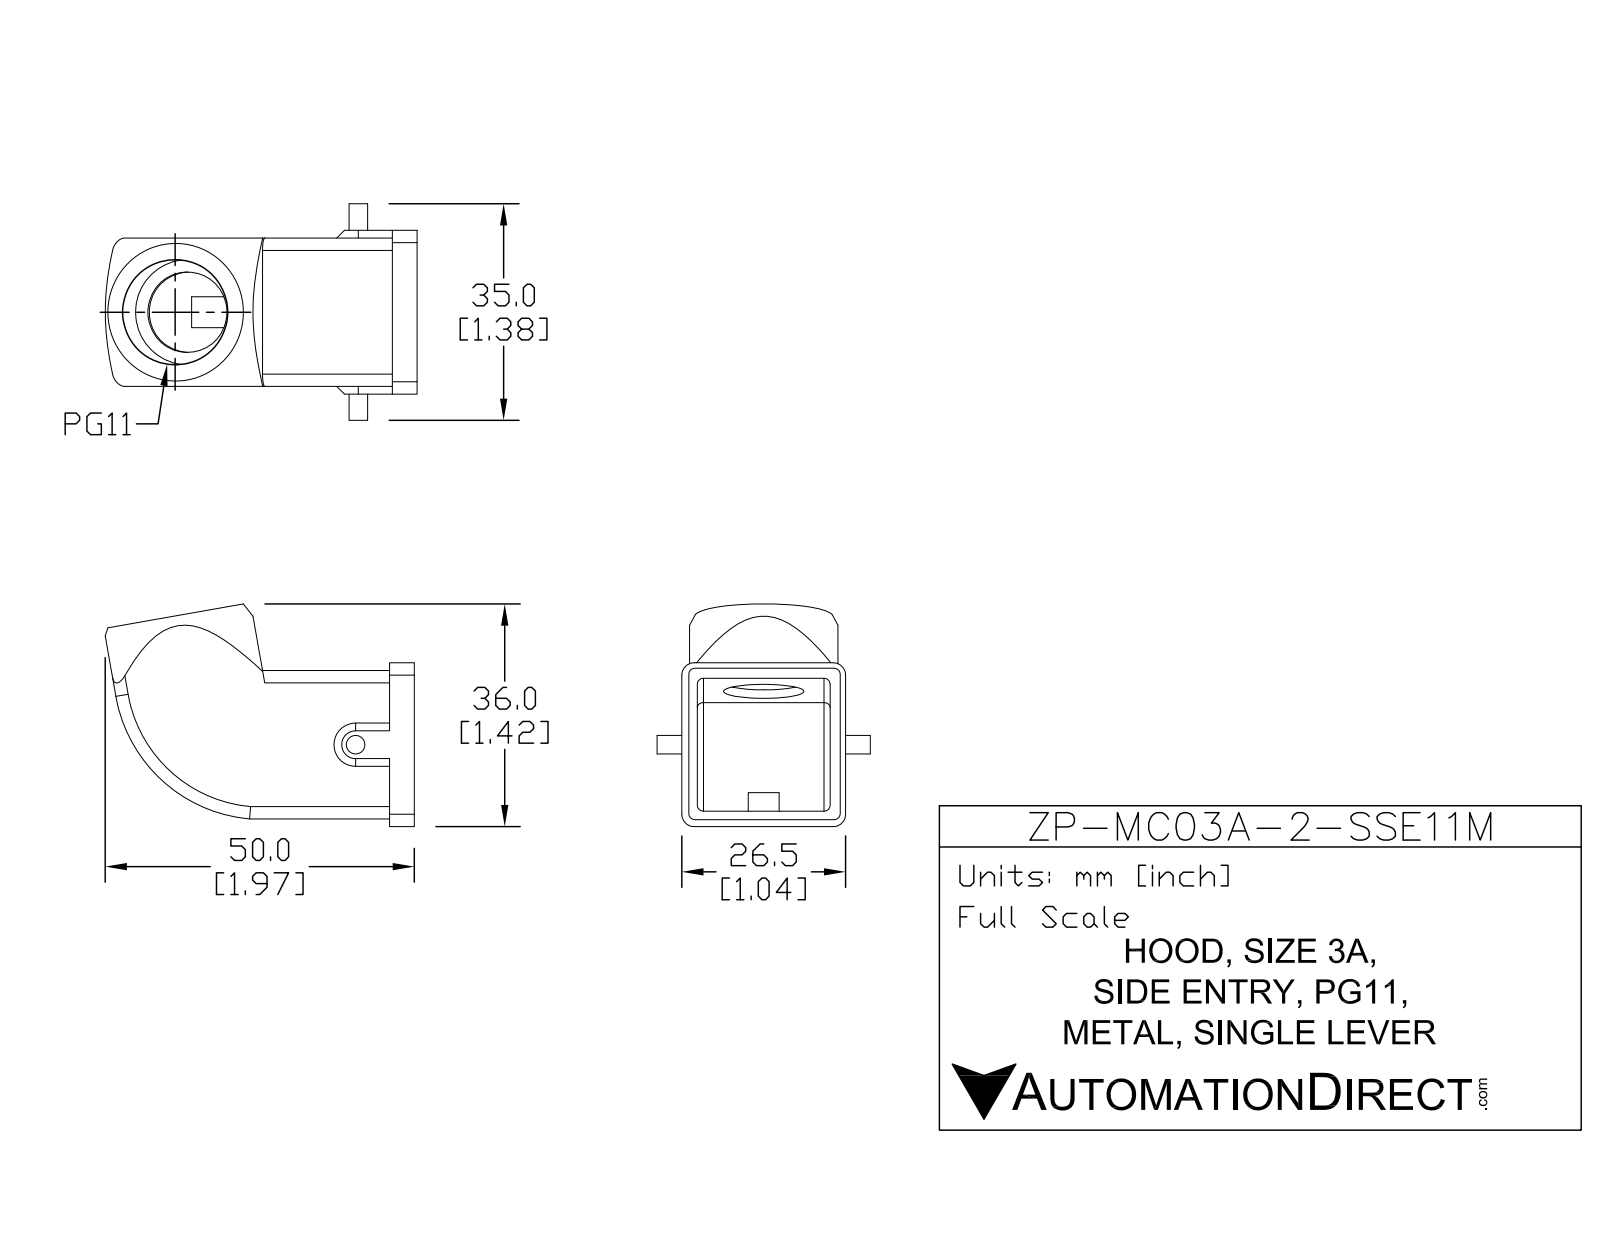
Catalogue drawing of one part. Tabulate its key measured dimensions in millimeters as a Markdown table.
| quantity | value |
| --- | --- |
| part name | ZP-MC03A-2-SSE11M |
| STEP written by | SolidWorks 2011 (AUTOMOTIVE_DESIGN) |
| units | millimeters |
| bodies | 1 solid, 72 faces (37 planar, 27 cylindrical, 8 other) |
| overall size | 47.95 × 36.02 × 34.5 |
| volume | 8 590 mm³ |
| surface area | 9 733 mm² |
| round holes (diameter × count) | 3 × 1, 13 × 1, 17 × 1 |
| round bosses / shafts (diameter × count) | 3 × 1 |
| partial cylindrical surfaces (radius × count) | 1 × 10, 2 × 10, 22.84 × 1, 24.09 × 1 |
| main face-to-face distances | 1.25, 22.75, 24, 21.5, 2.5, 25.25, 26.5, 12.41, 24.5, 24.09 |
